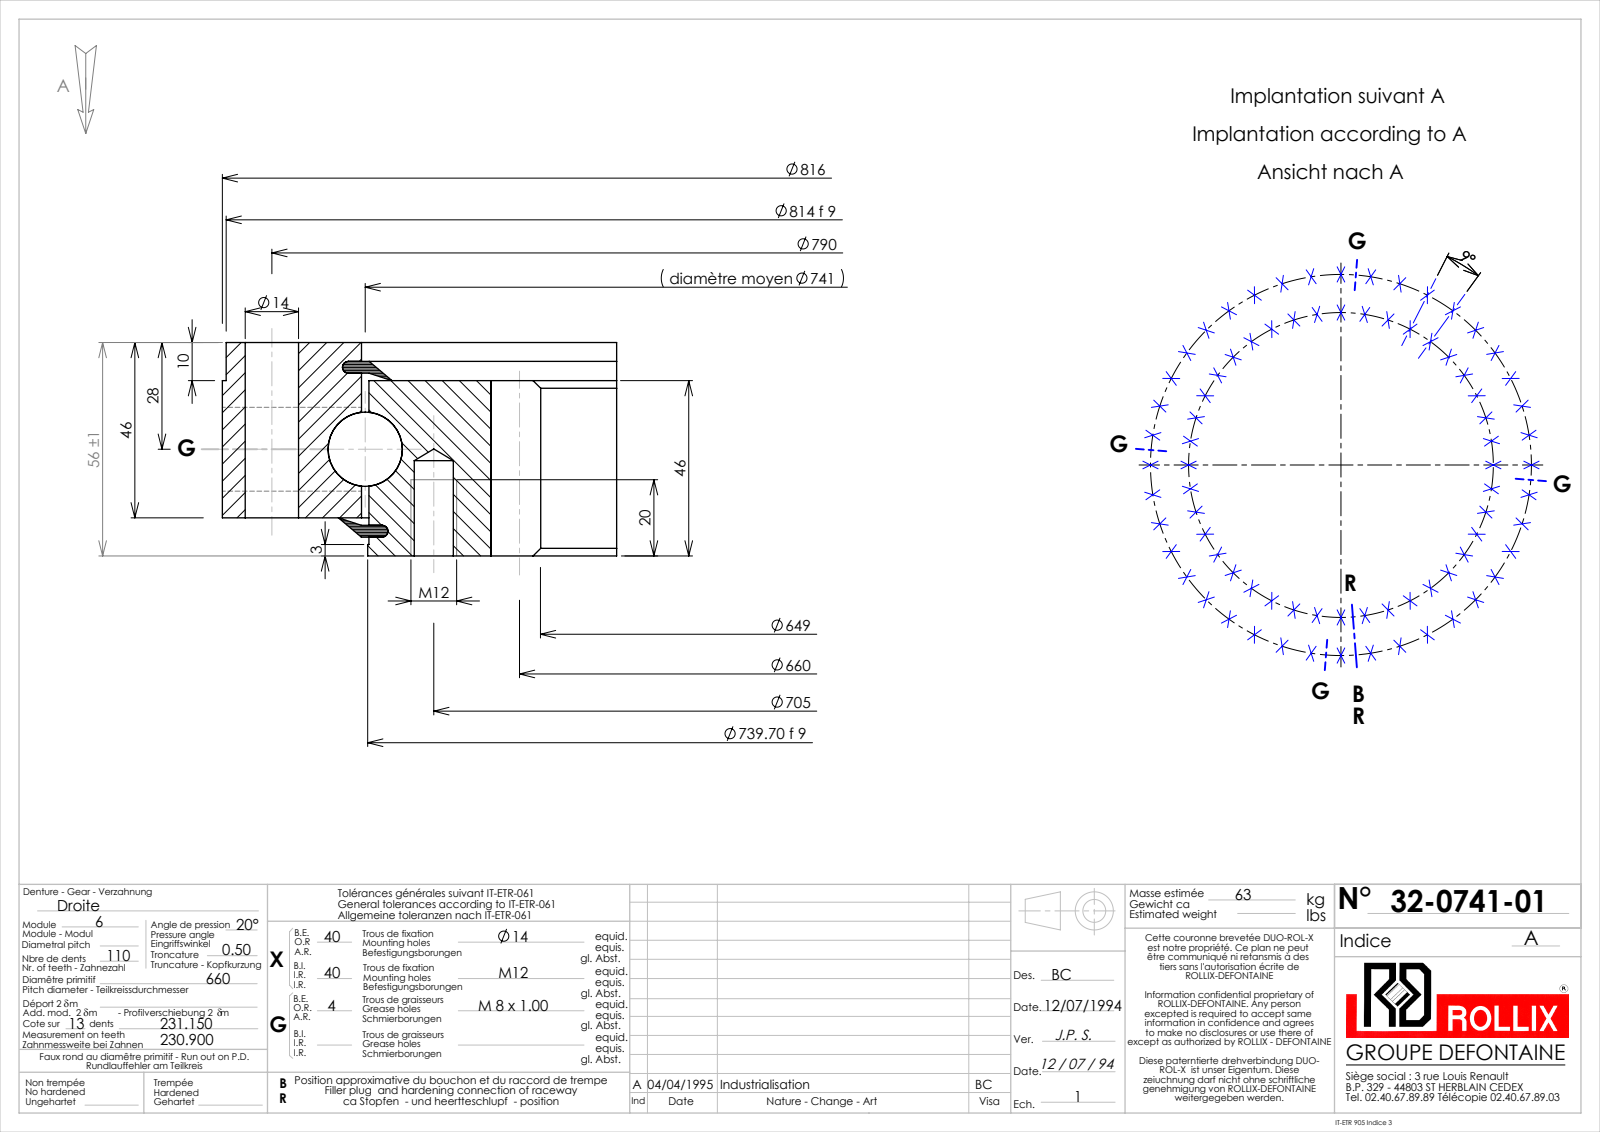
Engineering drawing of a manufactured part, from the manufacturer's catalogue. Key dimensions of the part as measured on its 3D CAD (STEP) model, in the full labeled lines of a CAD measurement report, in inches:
Part name (STEP PRODUCT): 32-0741-01
STEP written by: SolidWorks 2016 (CONFIG_CONTROL_DESIGN)
Units: inches
Bodies: 9 solids, 1057 faces (274 planar, 415 cylindrical, 368 other)
Overall size (bounding box): 32.796 × 32.796 × 2.205
Volume: 435.2 in³ · Surface area: 1 857 in²
Round holes (diameter × count): ⌀0.404 ×40, ⌀0.551 ×40, ⌀0.276 ×4, ⌀29.25 ×1
Round bosses / shafts (diameter × count): ⌀0.315 ×4, ⌀32.126 ×1, ⌀32.047 ×1, ⌀29.122 ×1, ⌀29.096 ×1
Partial cylindrical surfaces — rounded edges, fillets, slot ends (radius × count): R12.776 ×1, R13.287 ×1
Main face-to-face distances: 0.394, 1.811, 1.417, 2.205, 0.077, 0.199, 1.693, 0.317, 1.888, 1.494
Hole centre spacings: 6.48, 18.026, 4.342, 16.315, 27.67, 14.502, 19.626, 22.455
